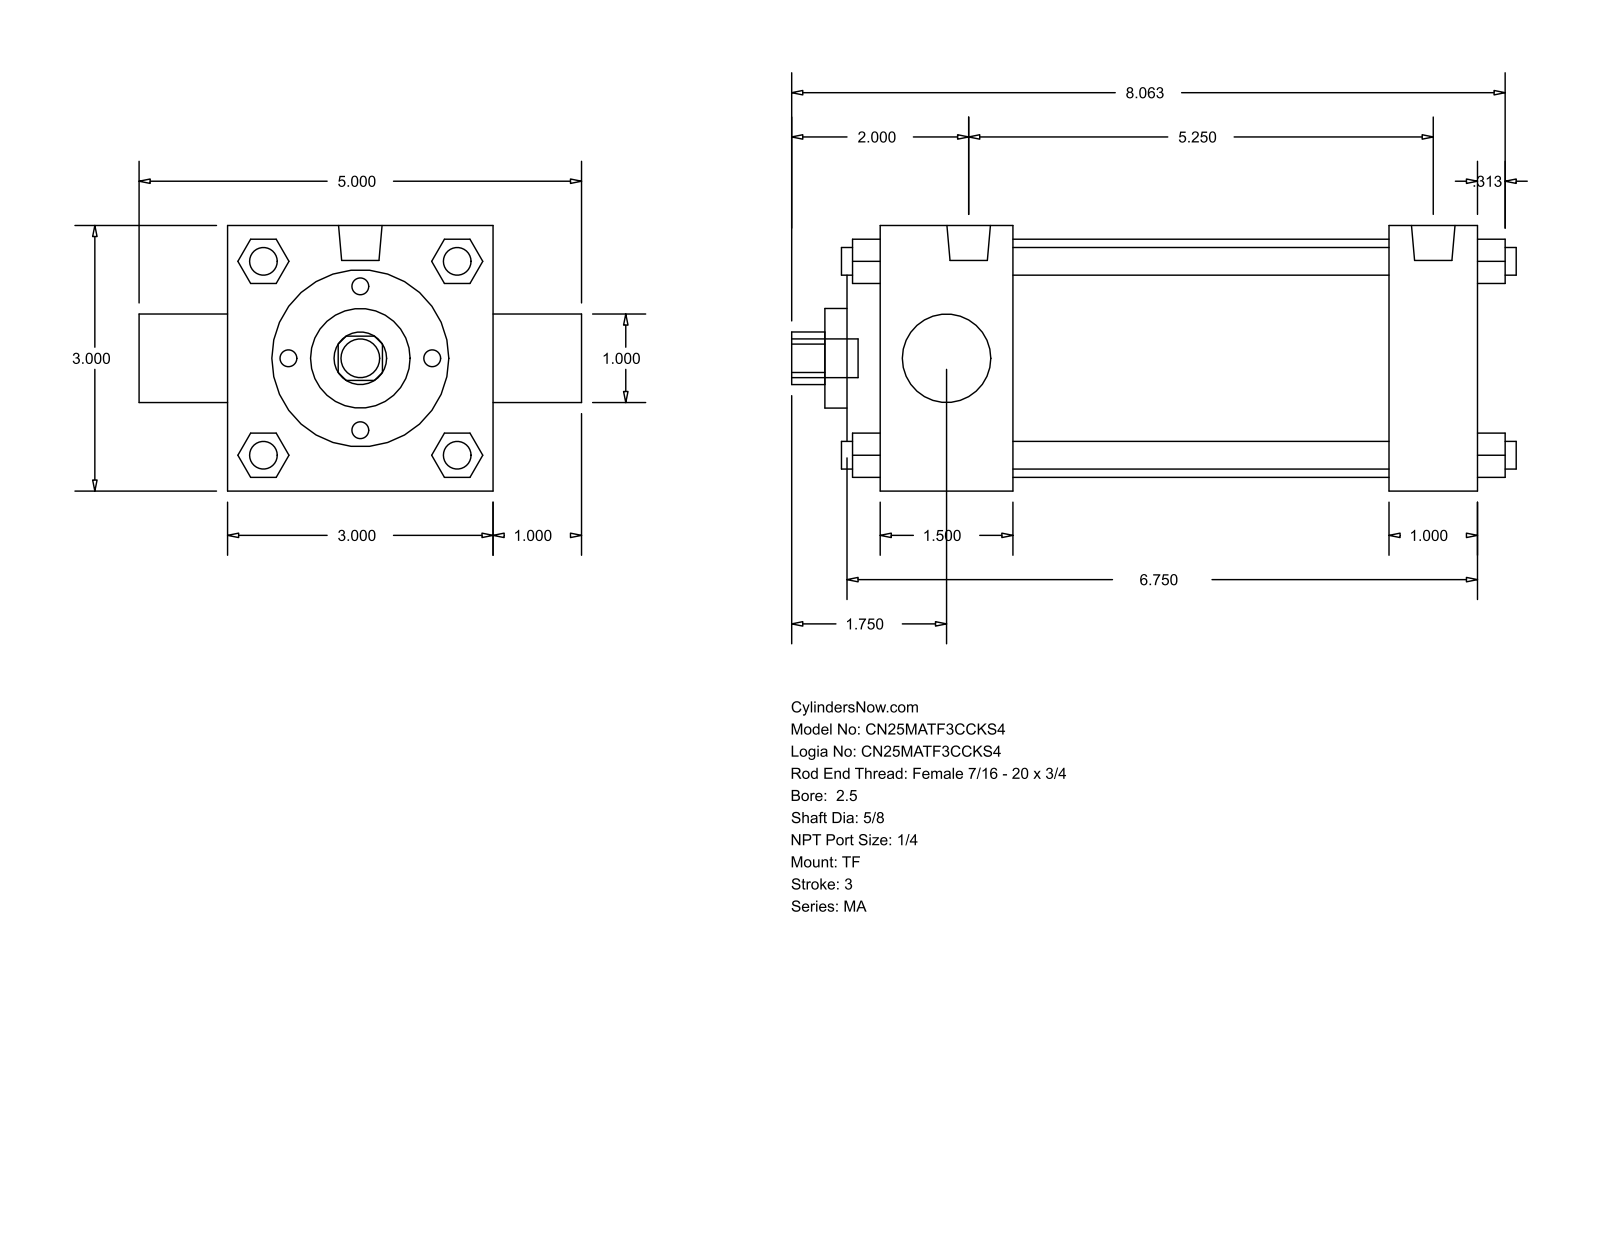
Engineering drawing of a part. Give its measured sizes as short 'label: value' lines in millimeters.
name: MA_TF__0250_0.625
written by: GSSL Pune (CONFIG_CONTROL_DESIGN)
unit: mm
bodies: 0 solids, 122 faces (93 planar, 29 cylindrical, 0 other)
size: 207.96 × 127 × 76.2
holes: 1× ⌀15.88, 1× ⌀25.4, 1× ⌀28.57, 1× ⌀50.8, 1× ⌀68.33
bosses: 7× ⌀7.94, 2× ⌀12.49, 1× ⌀11.11
rounds: 1× R7.54
face distances: 76.2, 171.45, 25.4, 38.1, 146.05, 107.95, 133.35, 12.7, 9.52, 47.62
